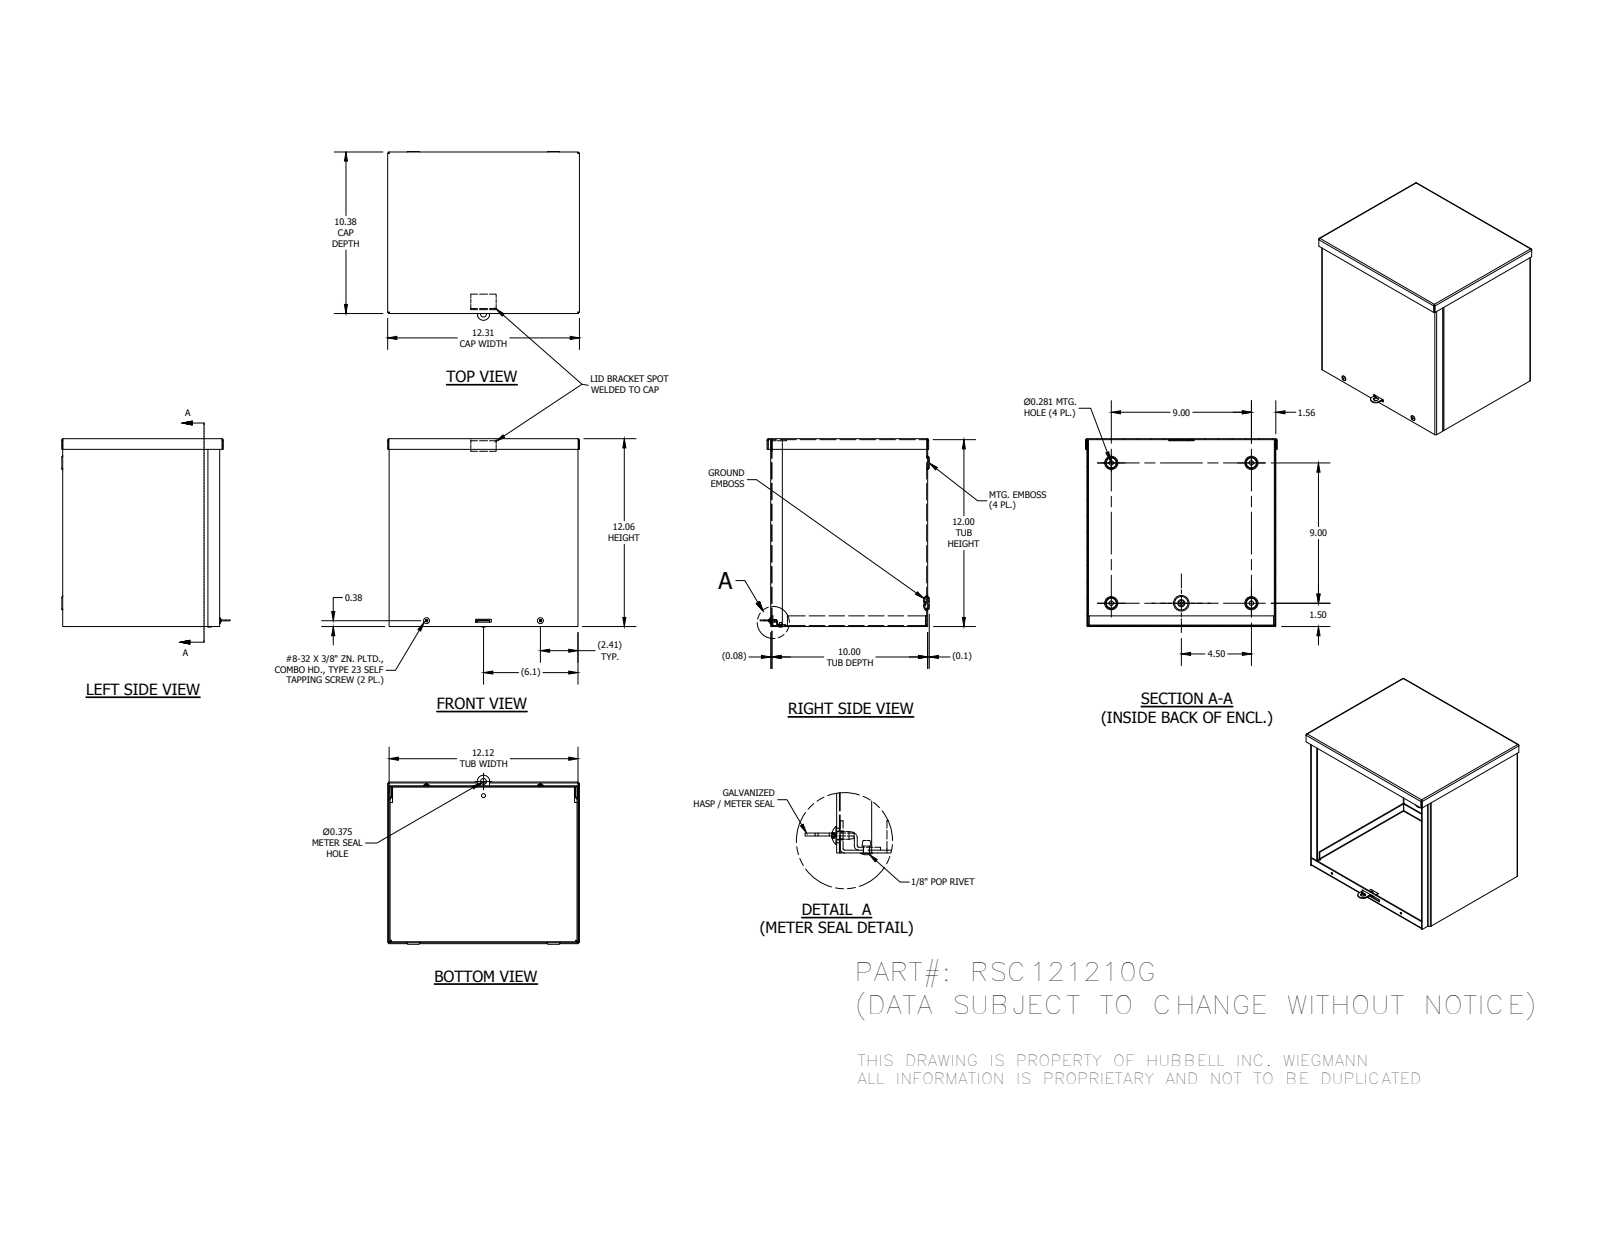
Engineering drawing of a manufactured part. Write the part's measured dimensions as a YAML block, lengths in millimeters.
part_name: "RSC121210GBKPA; RSC1210GEWPA; RSC1212GLFA; RSC1210GCPA (+5 more)"
step_written_by: "Autodesk Inventor 2014 (AUTOMOTIVE_DESIGN)"
units: millimeters
bodies: {solids: 9, faces: 320, planar: 183, cylindrical: 61, other: 76}
overall_size: [312.71, 307.39, 275.6]
volume: 862406
surface_area: 1105000
round_holes:
  - {diameter: 7.14, count: 4}
  - {diameter: 7.94, count: 4}
  - {diameter: 3.73, count: 2}
  - {diameter: 3.17, count: 1}
  - {diameter: 3.45, count: 1}
  - {diameter: 4.34, count: 1}
  - {diameter: 9.52, count: 1}
round_bosses_or_shafts:
  - {diameter: 9.75, count: 2}
  - {diameter: 4.17, count: 2}
  - {diameter: 6.65, count: 1}
  - {diameter: 5.93, count: 1}
  - {diameter: 3.17, count: 1}
partial_cylinders:
  - {radius: 0.79, count: 19}
  - {radius: 2.37, count: 18}
  - {radius: 2.67, count: 1}
  - {radius: 10.16, count: 1}
face_to_face_distances: [1.57, 304.8, 306.37, 254.4, 255.97, 252.83, 303.23, 307.94, 1.58, 6.41]
hole_center_spacings: [209.13, 330.24, 185.74, 97.17, 228.6, 35.71, 35.72, 258.06]
